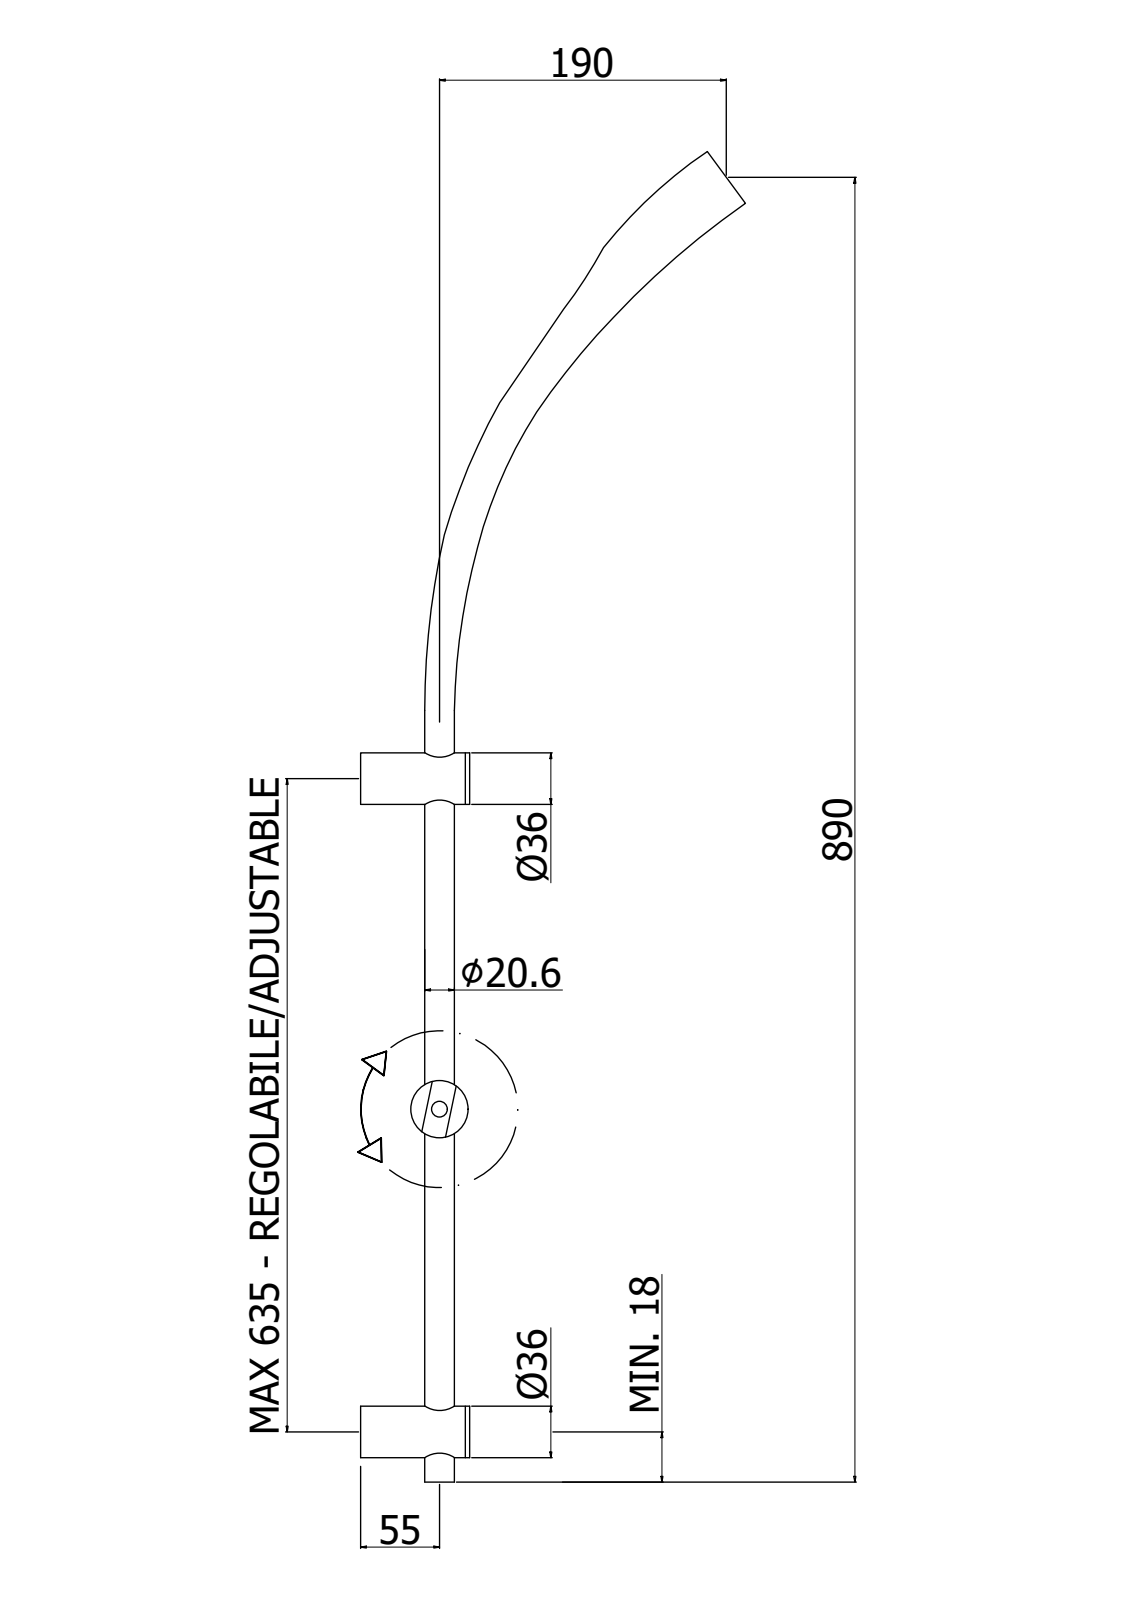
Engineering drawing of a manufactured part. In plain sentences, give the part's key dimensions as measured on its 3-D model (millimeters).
The part is named "M50540-016_3; M50380-030_1; M50380-032_2; M50520-011_2 (+8 more)". Its 3-D file was written by "CREO PARAMETRIC BY PTC INC, 2020044 (CONFIG_CONTROL_DESIGN)". It is 26 solids with 1176 faces: 430 planar, 367 cylindrical and 379 other. Overall it measures 902.71 by 252.18 by 109.44 millimeters. Its volume is 240 885 cubic millimeters and its surface area 271 734 square millimeters. Round holes: 5 of diameter 2, 2 of diameter 4, 2 of diameter 4.1, 2 of diameter 5.4, 2 of diameter 11.2, 2 of diameter 16.2, 2 of diameter 27, 2 of diameter 31, 1 of diameter 3, 1 of diameter 3.3, 1 of diameter 4.4, 1 of diameter 9.2. Round bosses or shafts: 2 of diameter 36.5, 2 of diameter 35, 2 of diameter 31.2, 2 of diameter 19.8, 2 of diameter 10.92, 2 of diameter 10.5, 2 of diameter 8.92, 2 of diameter 7. Partial cylindrical surfaces (rounded edges, fillets, slot ends): 24 of radius 1, 12 of radius 0.5, 9 of radius 1.5, 6 of radius 0.3, 6 of radius 0.6, 4 of radius 2, 4 of radius 100, 3 of radius 21.5. The main face-to-face distances are 2.5, 192.9, 2, 1.1, 1.8, 1.5, 68, 19.9, 1.09, 66. The hole center spacings are 14, 300.33, 300, 28, 301.3, 3.6, 26.
